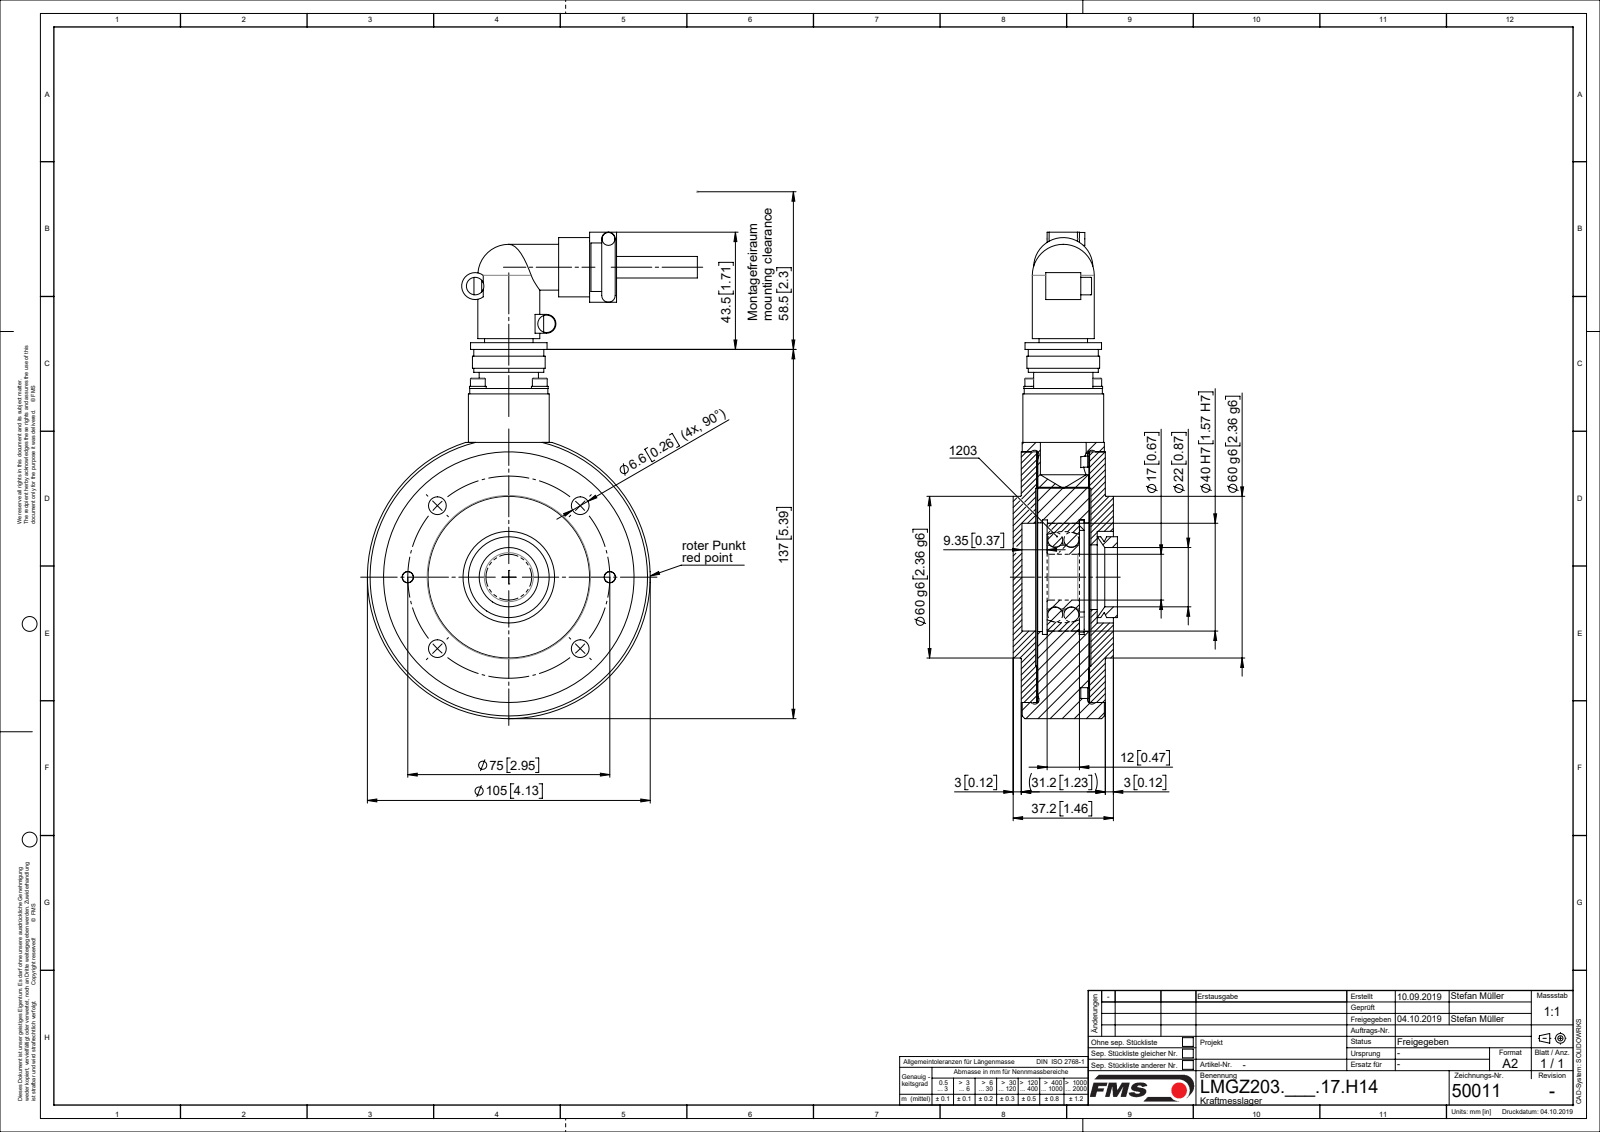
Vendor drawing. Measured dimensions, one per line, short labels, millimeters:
name: ZEICHNUNG3; L50011; L4795904; L47958(1) (+8 more)
written by: Mechanical Desktop 2007 (CONFIG_CONTROL_DESIGN)
unit: mm
bodies: 20 solids, 389 faces (123 planar, 223 cylindrical, 43 other)
size: 180.5 × 122.5 × 37.2
volume: 296 255 mm³; area: 105 621 mm²
holes: 4× ⌀2.6, 4× ⌀3.2, 4× ⌀3.4, 4× ⌀3.5, 4× ⌀6.6, 2× ⌀4, 2× ⌀5.3, 2× ⌀5.5, 2× ⌀10, 1× ⌀17, 1× ⌀22, 1× ⌀23
bosses: 4× ⌀6.2, 4× ⌀5.5, 4× ⌀3, 3× ⌀8, 2× ⌀22, 2× ⌀6.5, 2× ⌀5, 2× ⌀4.8
rounds: 2× R2.5, 1× R2, 1× R3.5, 1× R5
face distances: 19.25, 19, 5.85, 25.1, 6.1, 25.35, 19.5, 3, 20, 0.5
hole spacings: 37.5, 16.26, 23, 28.7, 53.04, 69.3, 32.53, 75.01
